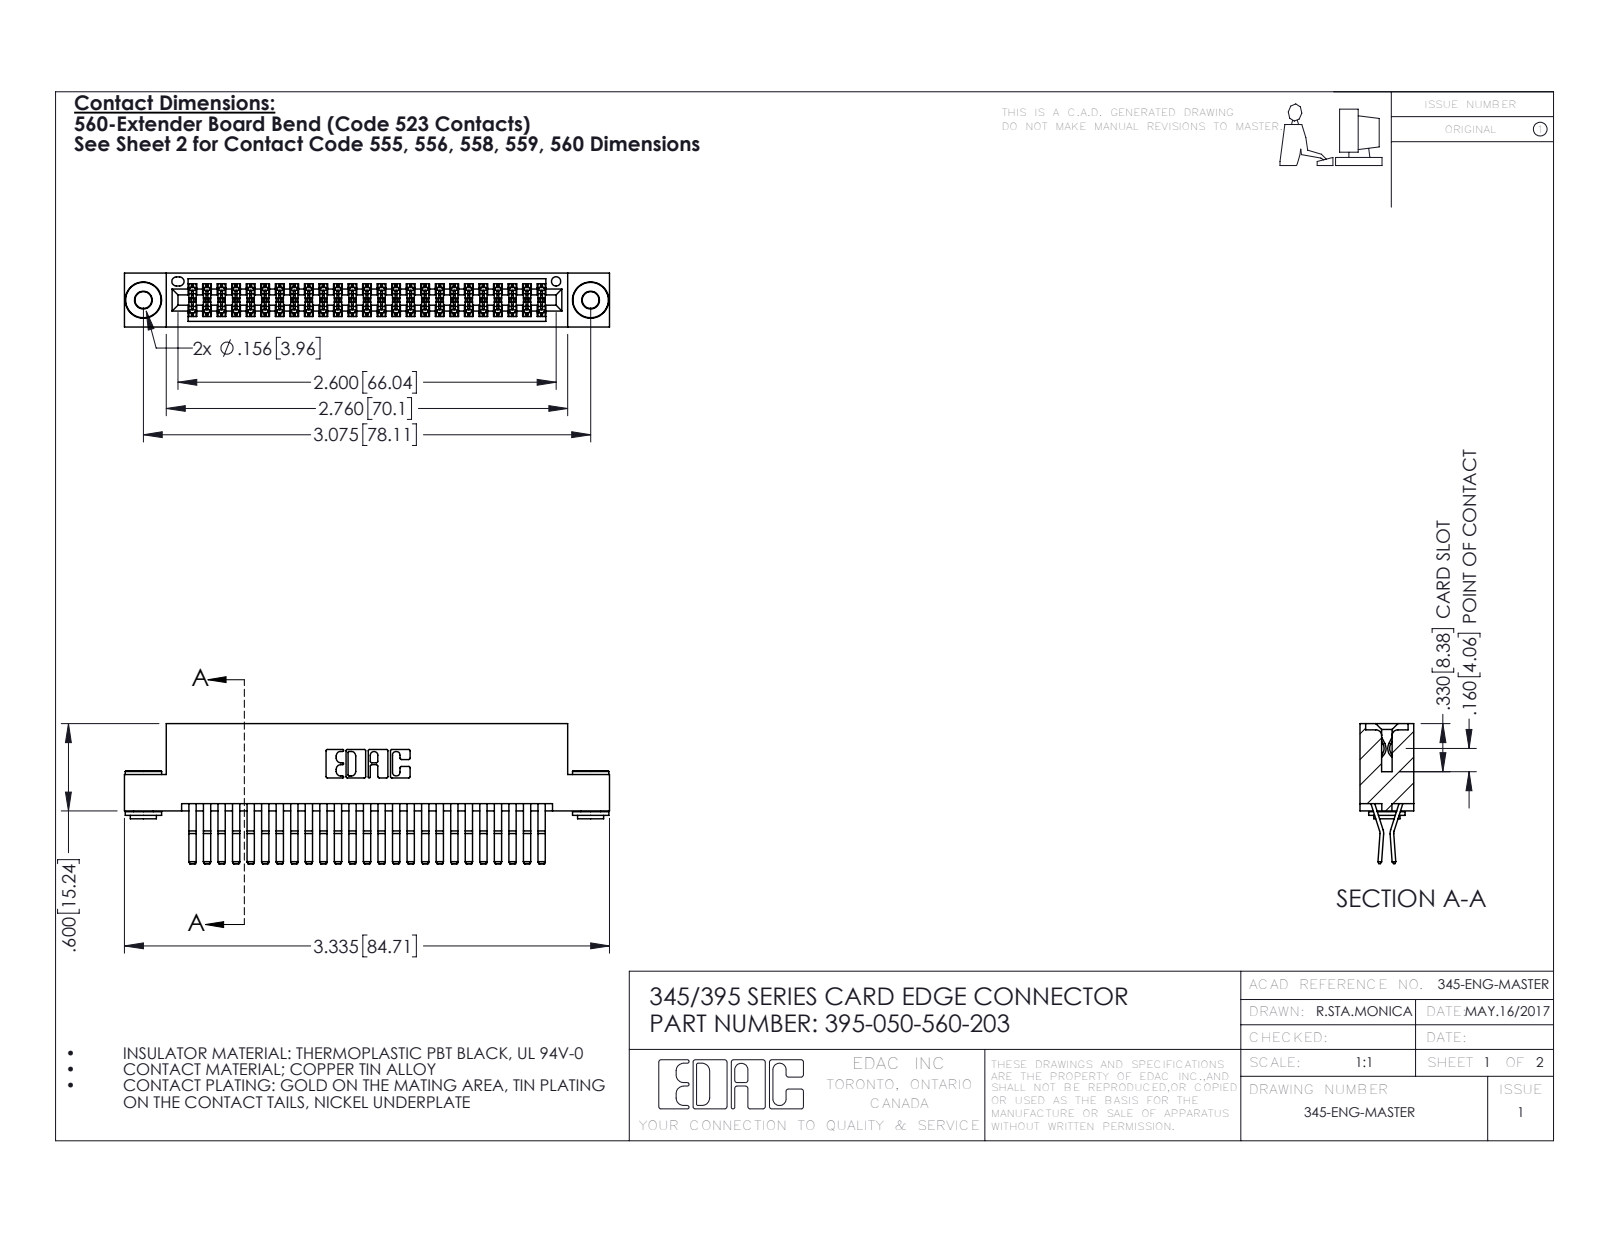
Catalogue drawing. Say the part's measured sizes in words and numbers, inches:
The part is named "345 Part_Flush Mounting Lugs - 0.156 Dia-TH; 345-250-002_345-250-002-102; 395-050-560-203; 345-292-001_560 Tail". Its 3-D file was written by "SolidWorks 2016 (CONFIG_CONTROL_DESIGN)". It is 53 solids with 2764 faces: 1740 planar, 1016 cylindrical and 8 other. Overall it measures 3.335 by 0.962 by 0.37 inches. Its volume is 0.514 cubic inches and its surface area 20.4 square inches. Round holes: 2 of diameter 0.116, 2 of diameter 0.156, 1 of diameter 0.064. Round bosses or shafts: 2 of diameter 0.25, 2 of diameter 0.18, 2 of diameter 0.136. Partial cylindrical surfaces (rounded edges, fillets, slot ends): 75 of radius 0.006, 22 of radius 0.01, 6 of radius 0.007, 6 of radius 0.031, 3 of radius 0.026, 2 of radius 0.01, 2 of radius 0.014, 2 of radius 0.019. The main face-to-face distances are 0.025, 0.072, 0.298, 0.2, 0.37, 0.098, 0.272, 0.225, 0.175, 0.149. The hole center spacings are 0.27, 2.84, 3.075.
